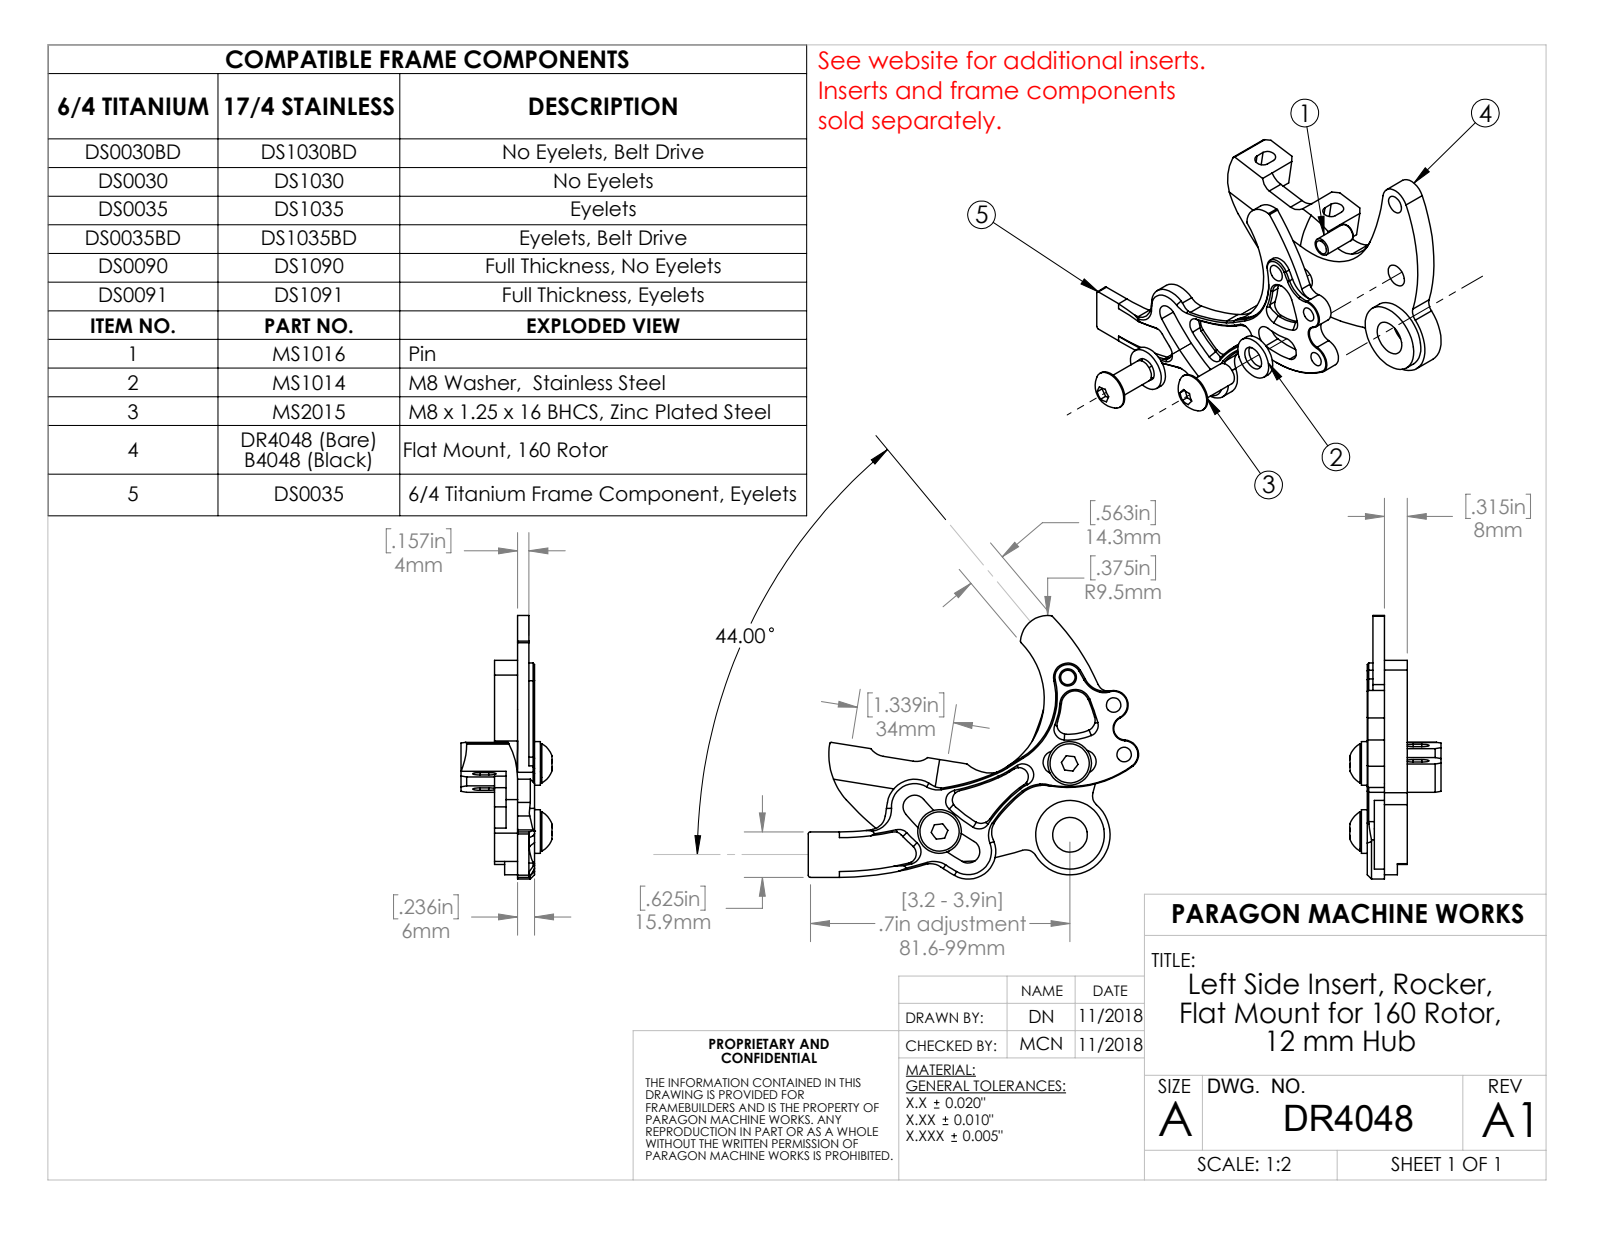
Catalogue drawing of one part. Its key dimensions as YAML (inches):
part_name: "DR4048"
step_written_by: "SolidWorks 2018 (AUTOMOTIVE_DESIGN)"
units: inches
bodies: {solids: 1, faces: 119, planar: 39, cylindrical: 79, other: 1}
overall_size: [3.746, 2.922, 0.915]
volume: 1.468
surface_area: 19.94
round_holes:
  - {diameter: 0.315, count: 2}
  - {diameter: 0.252, count: 1}
  - {diameter: 0.477, count: 1}
round_bosses_or_shafts:
  - {diameter: 0.945, count: 1}
partial_cylinders:
  - {radius: 0.138, count: 15}
  - {radius: 0.157, count: 5}
  - {radius: 0.102, count: 4}
  - {radius: 0.256, count: 3}
  - {radius: 0.039, count: 2}
  - {radius: 0.787, count: 2}
  - {radius: 0.02, count: 1}
  - {radius: 0.187, count: 1}
face_to_face_distances: [0.157, 0.315, 0.138, 0.177, 0.453, 0.295, 0.393, 0.02, 0.463, 0.6]
hole_center_spacings: [0.981, 1.181, 1.795, 2.019, 2.162, 2.756]
